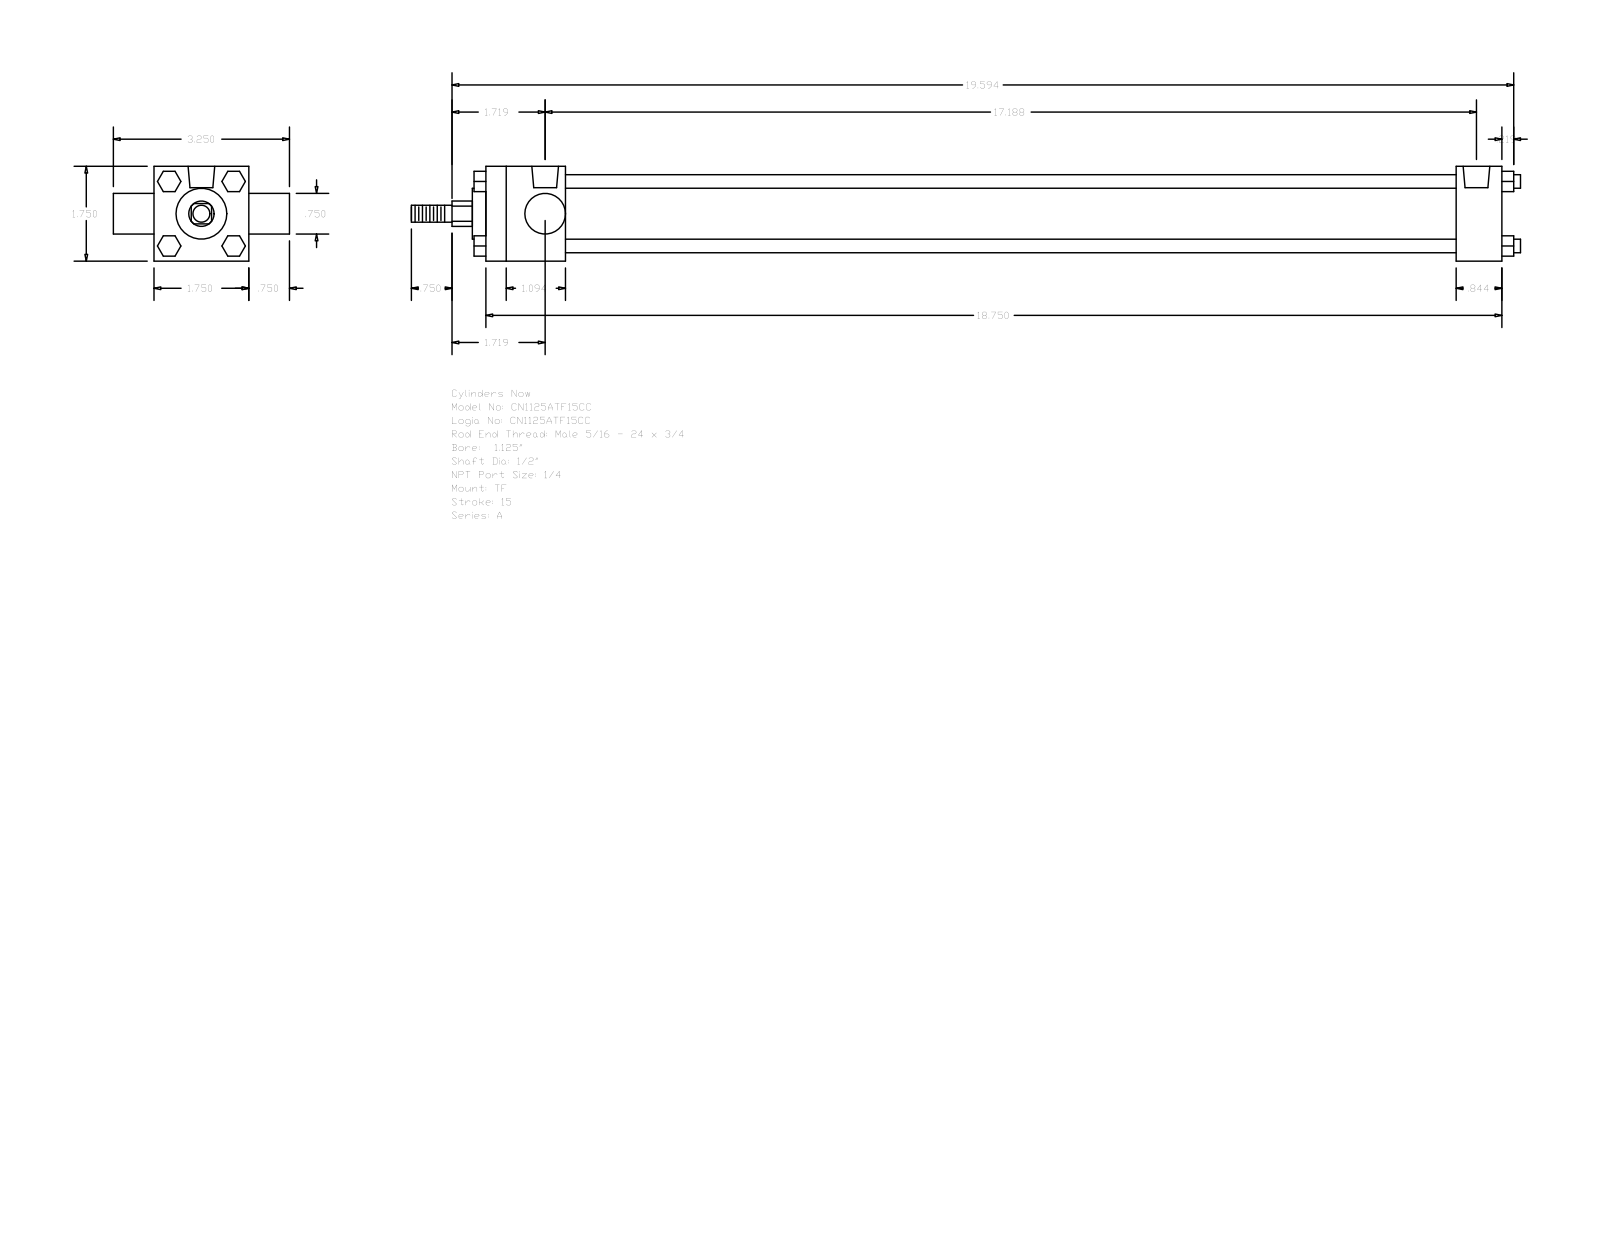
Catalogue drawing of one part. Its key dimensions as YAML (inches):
part_name: "A_TF__0112_0.5"
step_written_by: "GSSL Pune (CONFIG_CONTROL_DESIGN)"
units: inches
bodies: {solids: 0, faces: 120, planar: 92, cylindrical: 28, other: 0}
overall_size: [20.469, 3.25, 1.75]
round_holes:
  - {diameter: 0.219, count: 3}
  - {diameter: 0.492, count: 2}
round_bosses_or_shafts:
  - {diameter: 0.25, count: 4}
  - {diameter: 1.255, count: 1}
  - {diameter: 0.937, count: 1}
  - {diameter: 0.75, count: 1}
  - {diameter: 0.5, count: 1}
  - {diameter: 0.313, count: 1}
partial_cylinders:
  - {radius: 0.234, count: 1}
face_to_face_distances: [1.75, 18.75, 17.906, 0.844, 1.469, 16.437, 17.281, 0.75, 2.5, 0.375]
hole_center_spacings: [0.062, 0.063, 17.063, 17.125, 17.125, 17.187]
